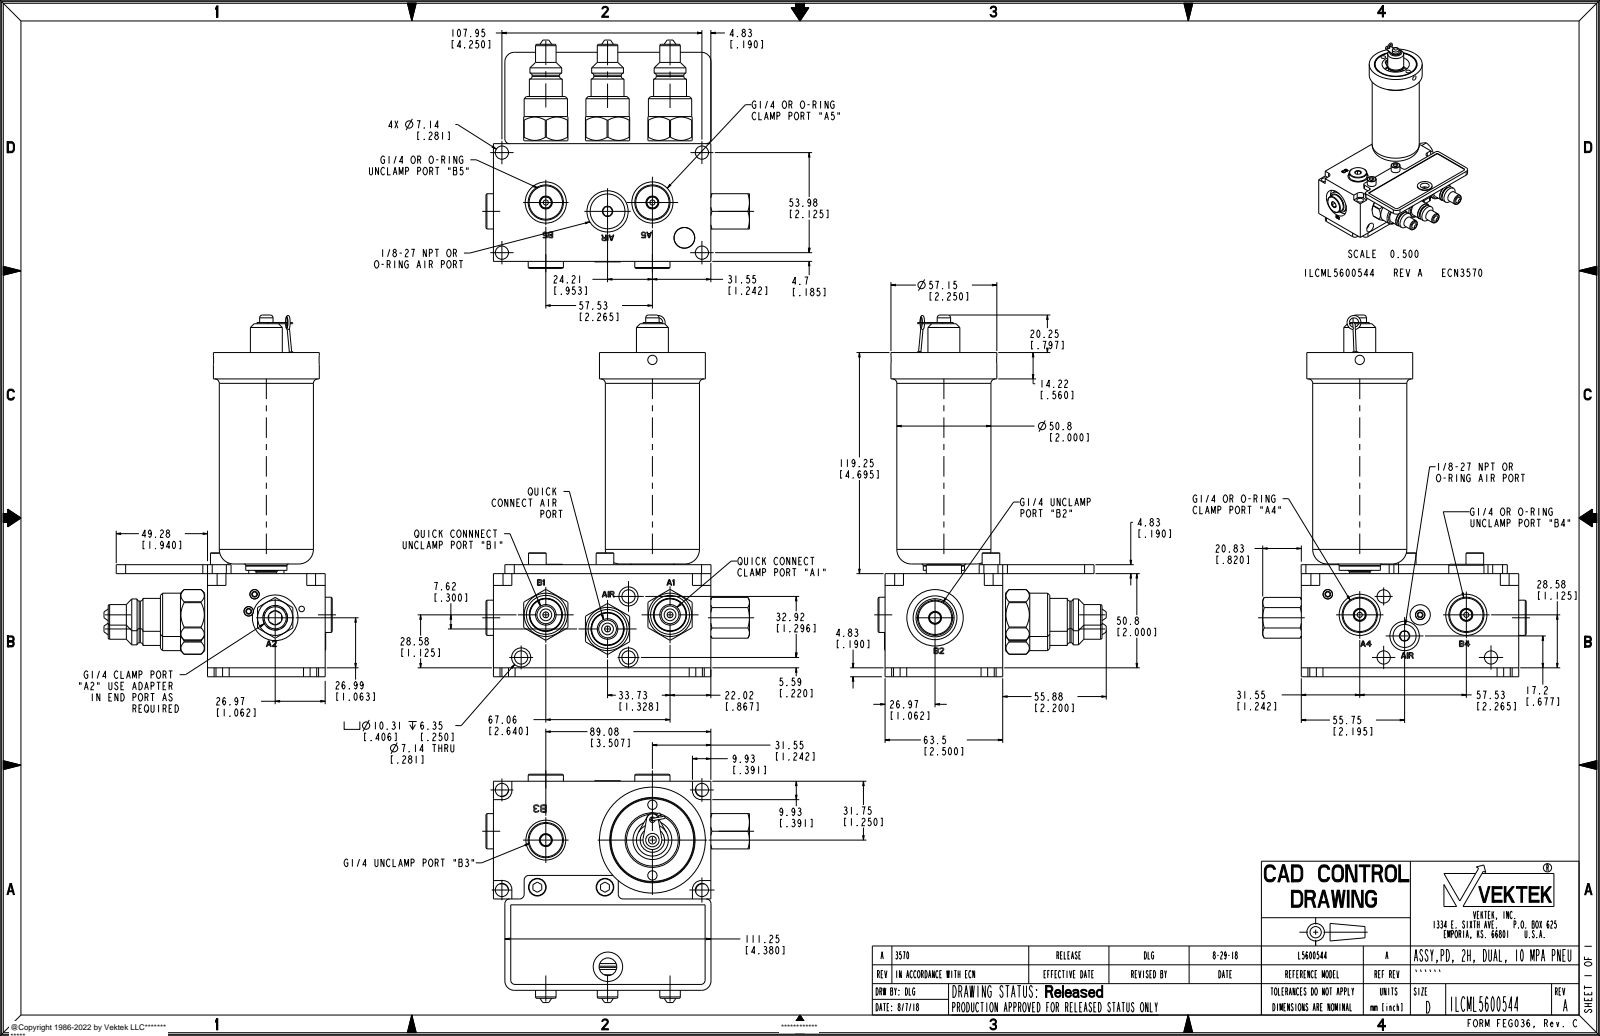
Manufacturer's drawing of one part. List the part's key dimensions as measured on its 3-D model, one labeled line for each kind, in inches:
Part name (STEP PRODUCT): ILCML5600544; 45600511; 30871966
STEP written by: PRO/ENGINEER BY PARAMETRIC TECHNOLOGY CORPORATION, 2013320 (CONFIG_CONTROL_DESIGN)
Units: inches
Bodies: 8 solids, 1854 faces (1094 planar, 370 cylindrical, 390 other)
Overall size (bounding box): 7.682 × 5.599 × 4.85
Volume: 35.9 in³ · Surface area: 213.1 in²
Round holes (diameter × count): ⌀0.281 ×8, ⌀0.875 ×5, ⌀0.123 ×4, ⌀0.202 ×4, ⌀0.197 ×3, ⌀0.406 ×3, ⌀0.514 ×3, ⌀0.079 ×2, ⌀0.118 ×2, ⌀0.468 ×2, ⌀0.846 ×2, ⌀1.25 ×2
Round bosses / shafts (diameter × count): ⌀0.748 ×5, ⌀0.197 ×4, ⌀0.177 ×4, ⌀0.92 ×3, ⌀0.699 ×3, ⌀0.675 ×3, ⌀0.585 ×3, ⌀0.436 ×3
Partial cylindrical surfaces — rounded edges, fillets, slot ends (radius × count): R0.09 ×70, R0.14 ×12, R0.1 ×6, R0.187 ×4, R0.2 ×3, R0.536 ×3, R0.812 ×2, R0.108 ×1
Main face-to-face distances: 2, 0.19, 2.19, 2.5, 0.17, 2.17, 2.36, 4.62, 0.02, 2.38
Hole centre spacings: 0.75, 0.752, 0.972, 2.125, 2.265, 2.322, 2.386, 4.25
